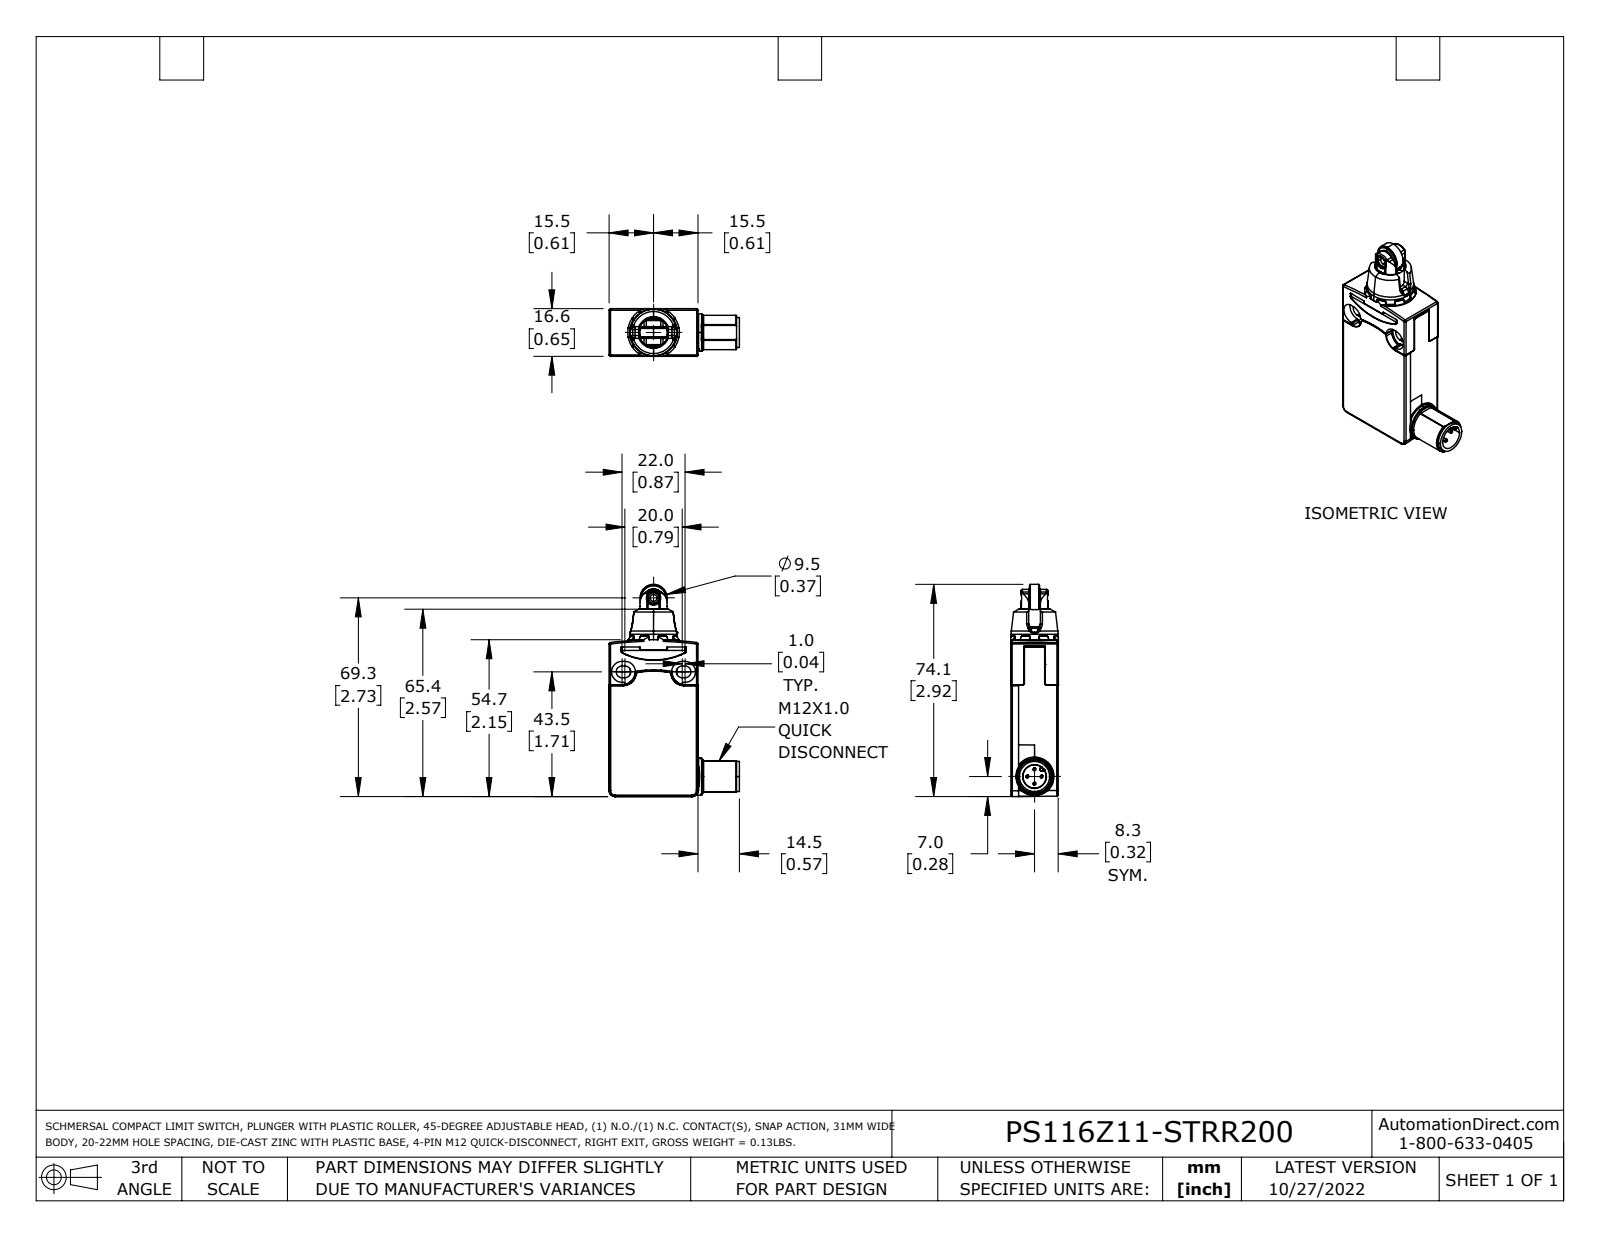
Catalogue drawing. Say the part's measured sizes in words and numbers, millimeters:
The part is named "PS116Z11-STRR200_Default". Its 3-D file was written by "SolidWorks 2021 (CONFIG_CONTROL_DESIGN)". It is 2 solids with 1089 faces: 307 planar, 476 cylindrical and 306 other. Overall it measures 74.1 by 45.5 by 16.6 millimeters. Its volume is 28 500 cubic millimeters and its surface area 12 890 square millimeters. Round holes: 1 of diameter 2, 1 of diameter 2.4, 1 of diameter 3.1, 1 of diameter 3.5, 1 of diameter 5, 1 of diameter 6.7, 1 of diameter 8.3, 1 of diameter 11.6, 1 of diameter 14.5. Round bosses or shafts: 4 of diameter 1, 2 of diameter 13, 1 of diameter 16.4, 1 of diameter 14.4, 1 of diameter 13.3, 1 of diameter 11.4, 1 of diameter 10.5, 1 of diameter 9.5. Partial cylindrical surfaces (rounded edges, fillets, slot ends): 120 of radius 0.2, 79 of radius 0.1, 42 of radius 0.5, 22 of radius 1, 10 of radius 0.4, 5 of radius 2, 4 of radius 2.1, 4 of radius 3. The main face-to-face distances are 16.5, 16.6, 31, 1.7, 3, 5.6, 2.9, 16.6, 3.5, 1. The hole center spacings are 41.
